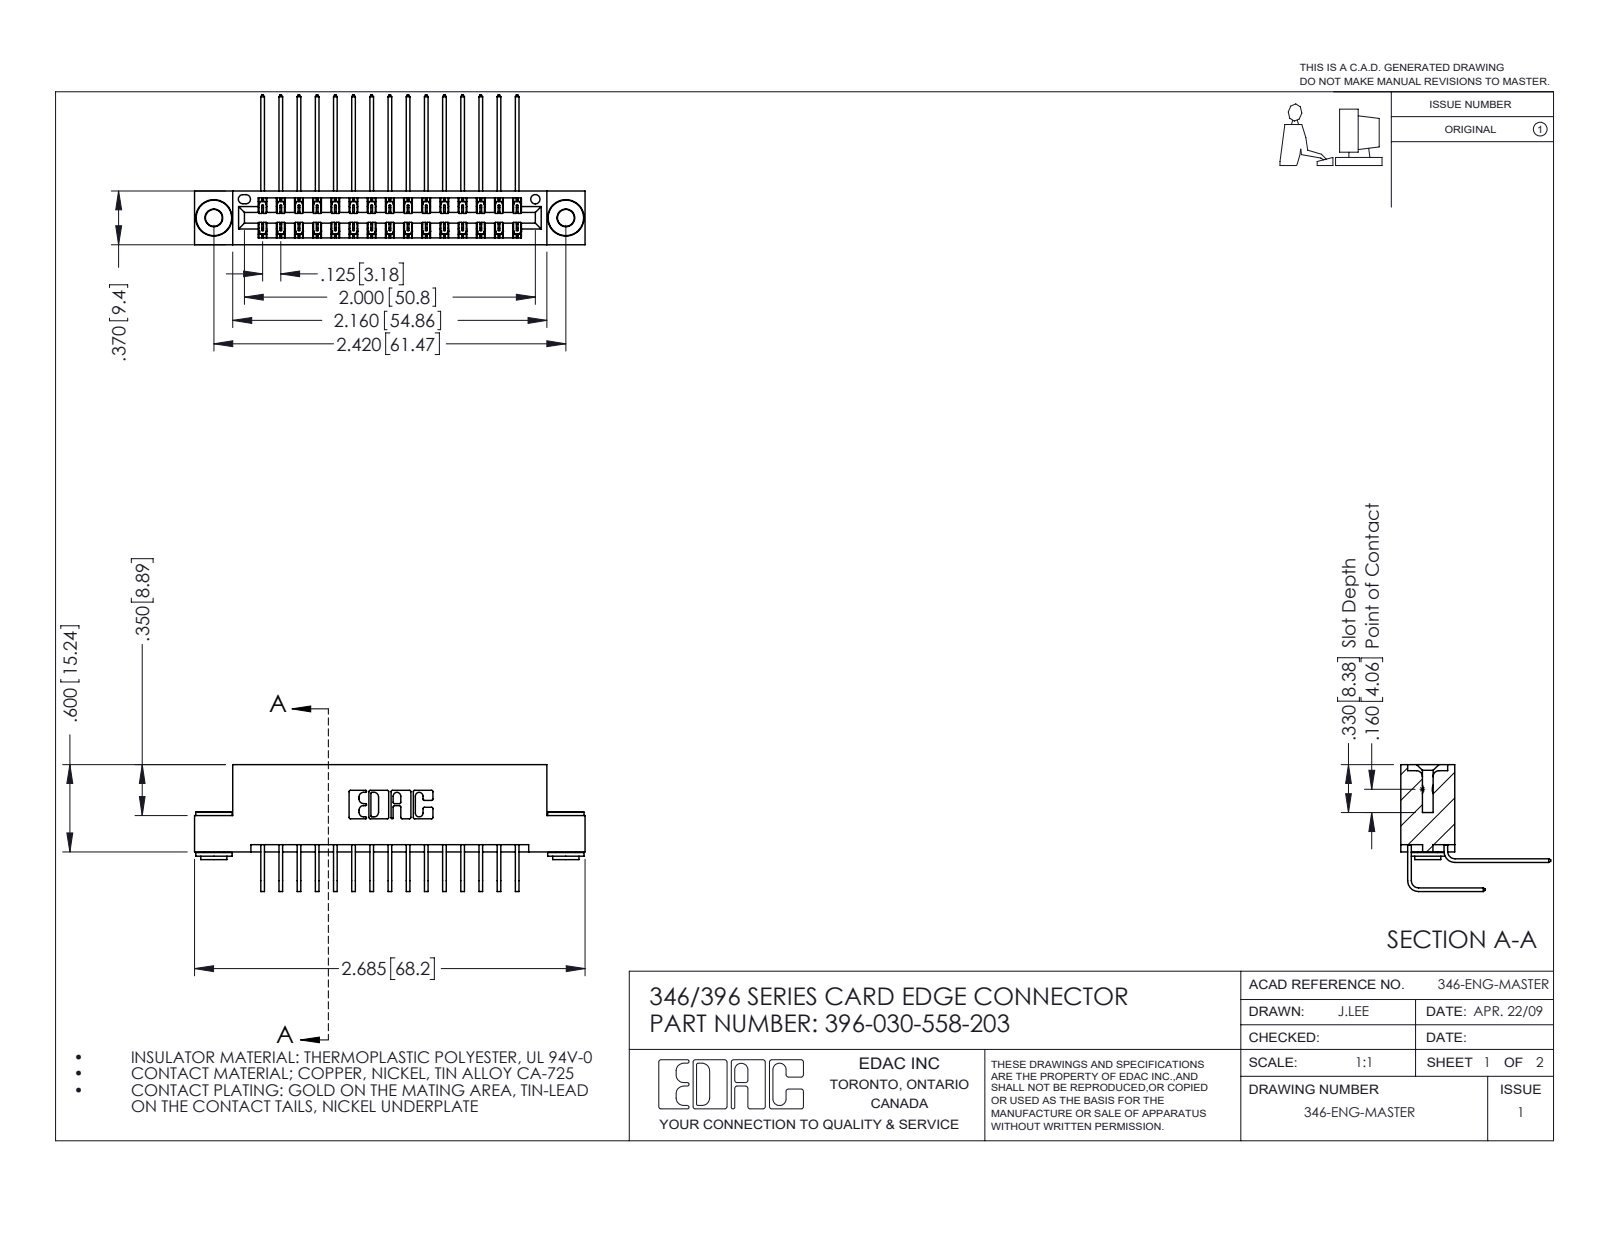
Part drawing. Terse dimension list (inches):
name: 345-292-001_558 559 Tail - 1; 345-250-002_345-250-002-102; 396-030-558-203; 346 Part_Flush Mounting Lugs - 0.156 Dia-TH (+1 more)
written by: SolidWorks 2016 (CONFIG_CONTROL_DESIGN)
unit: in
bodies: 33 solids, 1780 faces (1196 planar, 576 cylindrical, 8 other)
size: 2.685 × 1.03 × 0.873
volume: 0.405 in³; area: 15.09 in²
holes: 2× ⌀0.116, 2× ⌀0.156, 1× ⌀0.064
bosses: 2× ⌀0.25, 2× ⌀0.18, 2× ⌀0.136
rounds: 45× R0.006, 22× R0.01, 6× R0.007, 6× R0.031, 3× R0.026, 2× R0.014, 2× R0.022, 2× R0.024
face distances: 0.322, 0.048, 0.25, 0.025, 0.37, 0.298, 0.072, 0.275, 0.148, 0.222
hole spacings: 0.246, 2.213, 2.42
